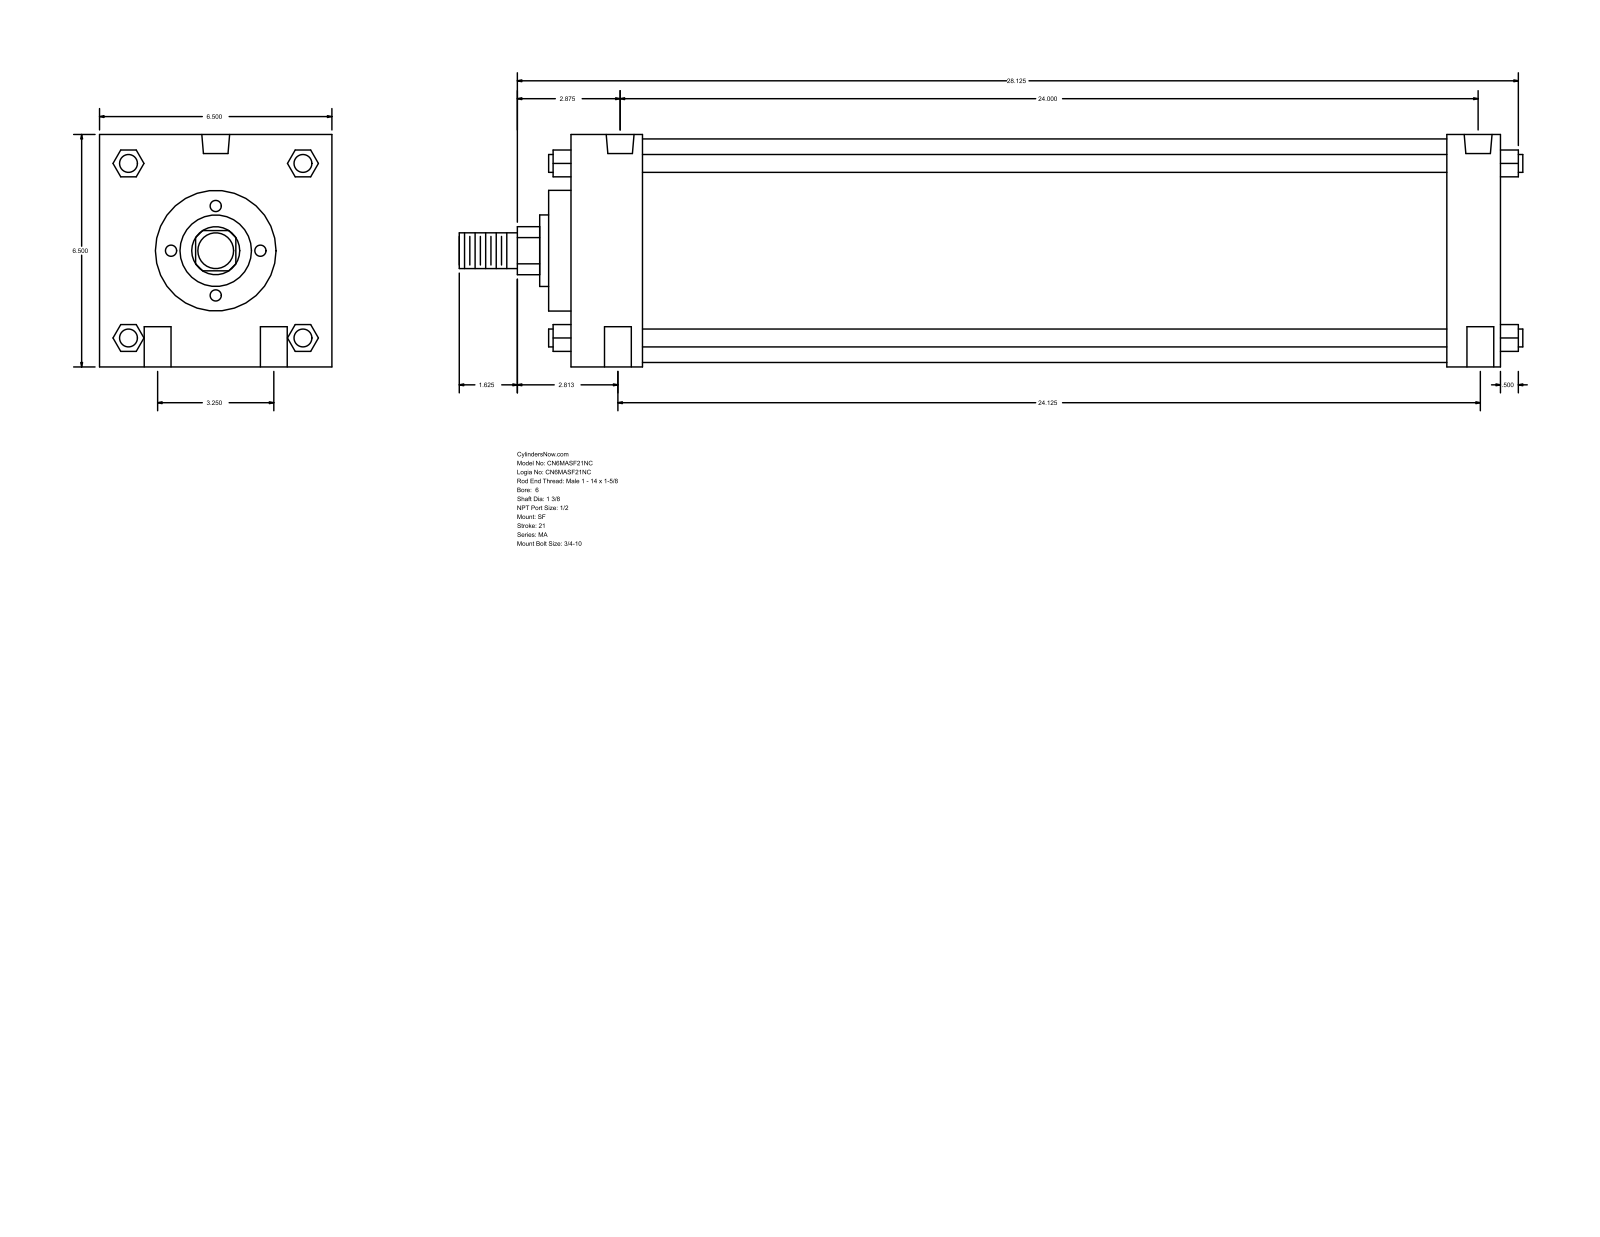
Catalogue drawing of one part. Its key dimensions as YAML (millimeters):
part_name: "MA_SF__0600_1.375"
step_written_by: "GSSL Pune (CONFIG_CONTROL_DESIGN)"
units: millimeters
bodies: {solids: 0, faces: 126, planar: 95, cylindrical: 31, other: 0}
overall_size: [755.65, 165.1, 165.1]
round_holes:
  - {diameter: 19.05, count: 4}
  - {diameter: 17.46, count: 2}
  - {diameter: 19.77, count: 2}
round_bosses_or_shafts:
  - {diameter: 12.7, count: 4}
  - {diameter: 158.75, count: 1}
  - {diameter: 85.72, count: 1}
  - {diameter: 50.8, count: 1}
  - {diameter: 34.92, count: 1}
  - {diameter: 25.4, count: 1}
partial_cylinders:
  - {radius: 17.06, count: 1}
face_to_face_distances: [165.1, 660.4, 622.3, 50.8, 38.1, 571.5, 609.6, 66.67, 15.87, 638.17]
hole_center_spacings: [41.3, 612.57, 82.54, 612.77, 618.3, 609.59, 609.6]
